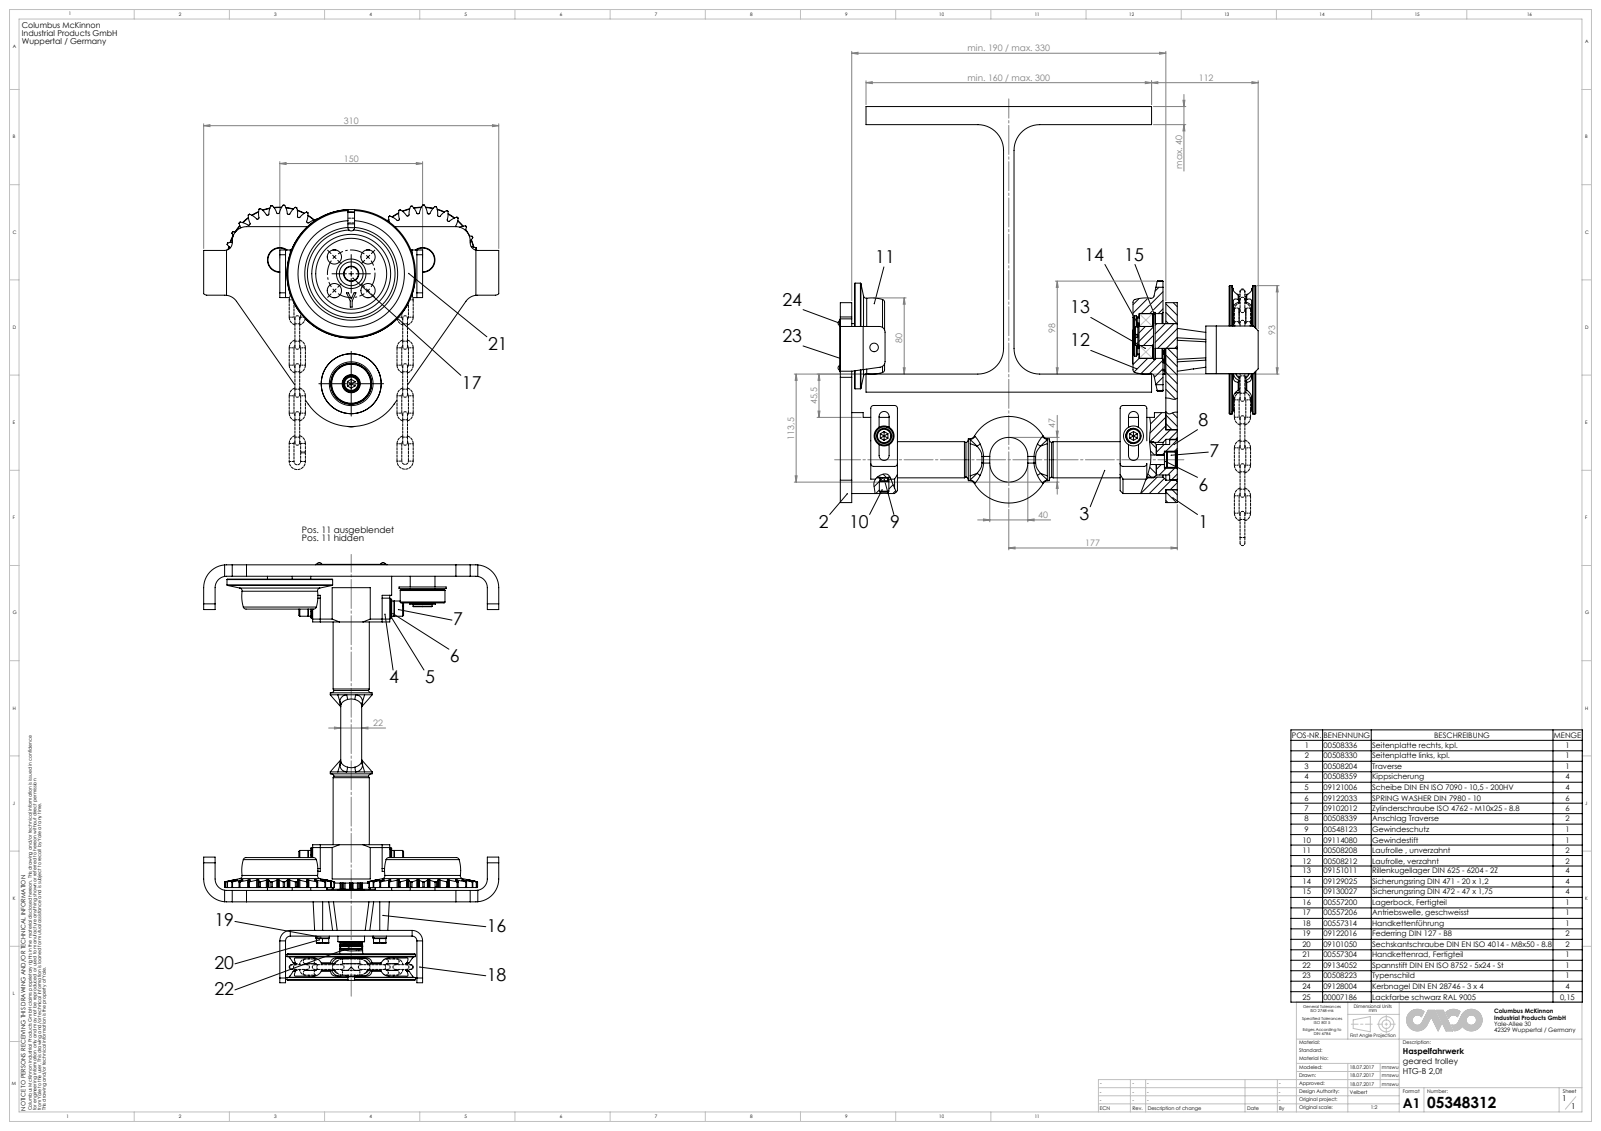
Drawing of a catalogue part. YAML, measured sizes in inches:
part_name: "HTG-B 2,0t"
step_written_by: "SolidWorks 2015 (AUTOMOTIVE_DESIGN)"
units: inches
bodies: {solids: 0, faces: 884, planar: 269, cylindrical: 373, other: 242}
overall_size: [18.157, 17.378, 12.205]
round_holes:
  - {diameter: 0.591, count: 4}
  - {diameter: 0.354, count: 2}
  - {diameter: 1.024, count: 2}
  - {diameter: 1.496, count: 2}
  - {diameter: 1.575, count: 2}
  - {diameter: 1.673, count: 2}
  - {diameter: 0.236, count: 1}
  - {diameter: 0.335, count: 1}
  - {diameter: 0.63, count: 1}
  - {diameter: 0.709, count: 1}
  - {diameter: 1.693, count: 1}
round_bosses_or_shafts:
  - {diameter: 0.197, count: 22}
  - {diameter: 0.63, count: 3}
  - {diameter: 4.37, count: 2}
  - {diameter: 1.063, count: 2}
  - {diameter: 0.827, count: 2}
  - {diameter: 0.787, count: 2}
  - {diameter: 0.394, count: 2}
  - {diameter: 5.315, count: 1}
partial_cylinders:
  - {radius: 0.787, count: 68}
  - {radius: 0.039, count: 45}
  - {radius: 0.059, count: 9}
  - {radius: 0.394, count: 9}
  - {radius: 0.118, count: 6}
  - {radius: 0.207, count: 4}
  - {radius: 0.236, count: 4}
  - {radius: 0.433, count: 4}
face_to_face_distances: [0.748, 11.063, 11.811, 0.472, 7.185, 6.752, 10.315, 13.465, 6.28, 6.713]
hole_center_spacings: [0.984, 1.392, 0.848, 1.969, 2.002, 2.26, 2.589, 3.007]
